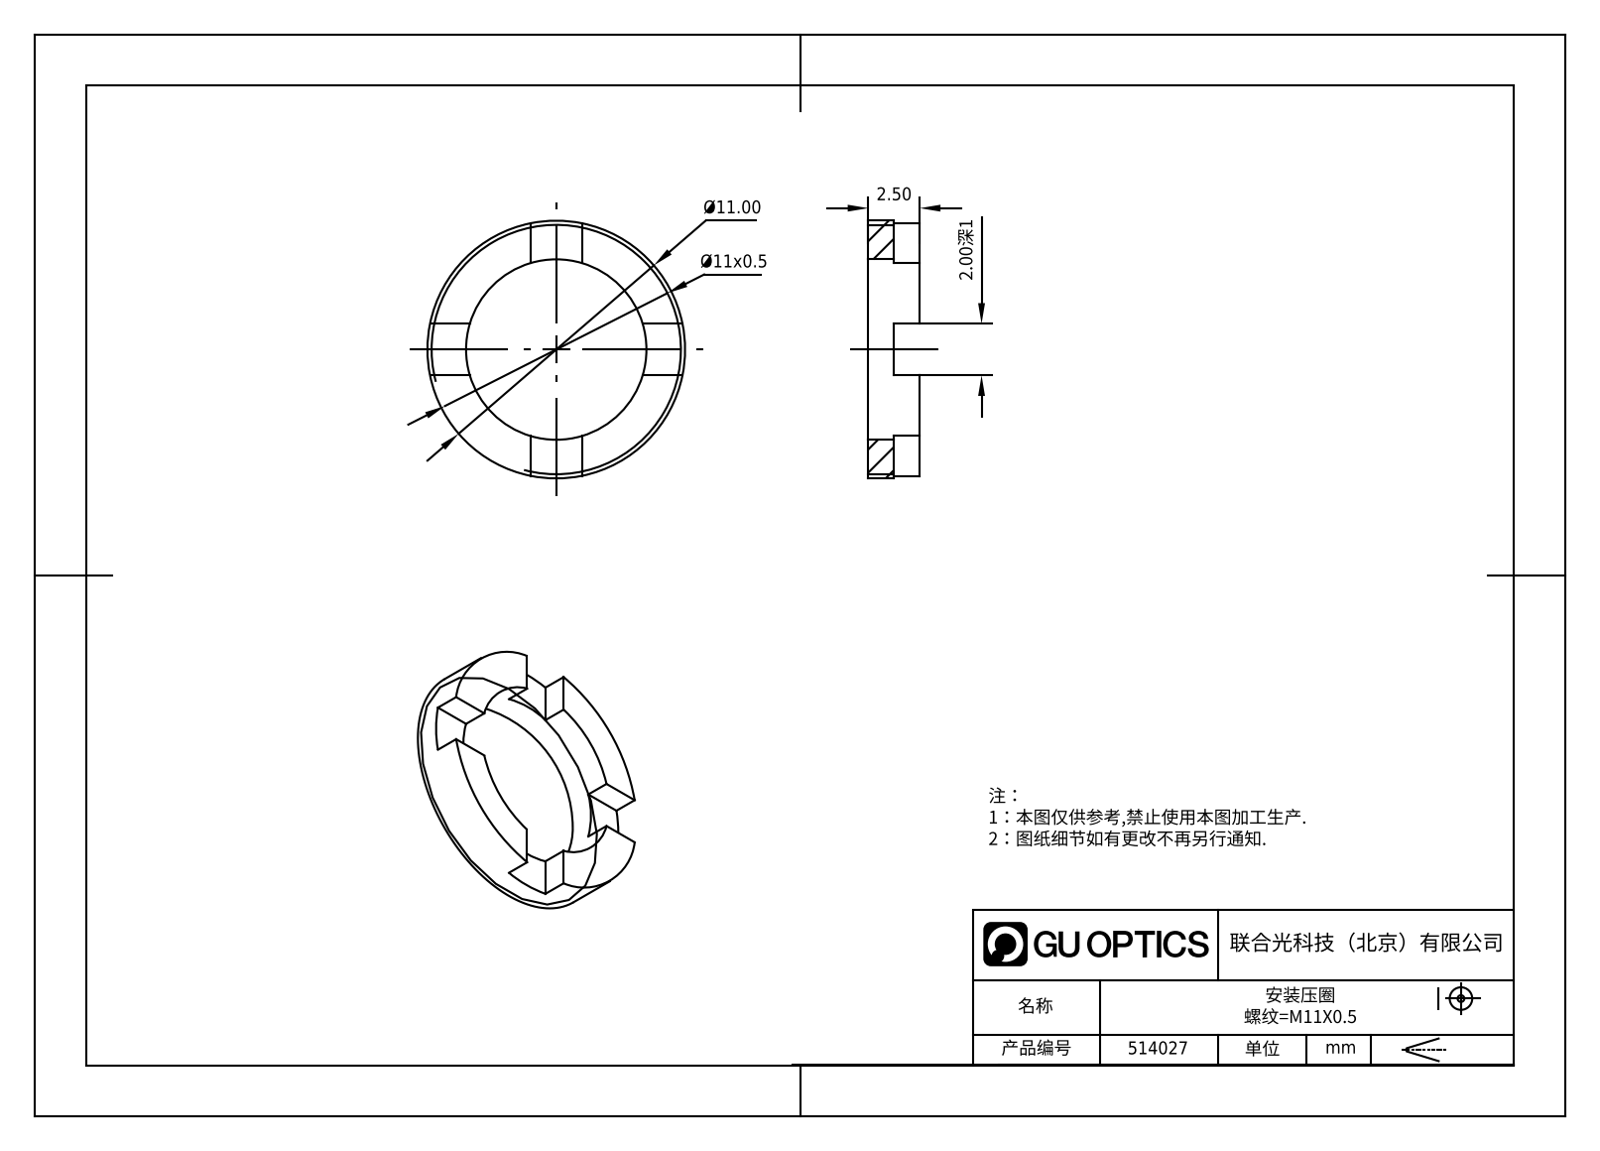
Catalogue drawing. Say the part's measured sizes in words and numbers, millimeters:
The part is named "514027". Its 3-D file was written by "SolidWorks 2020 (CONFIG_CONTROL_DESIGN)". It is 1 solid with 21 faces: 17 planar, 4 cylindrical and 0 other. Overall it measures 11 by 11 by 2.5 millimeters. Its volume is 102 cubic millimeters and its surface area 241 square millimeters. Round holes: 1 of diameter 8. Round bosses or shafts: 1 of diameter 11. The main face-to-face distances are 2.5, 1.5, 1, 2, 0.5, 6.5, 6, 4, 4.5.
